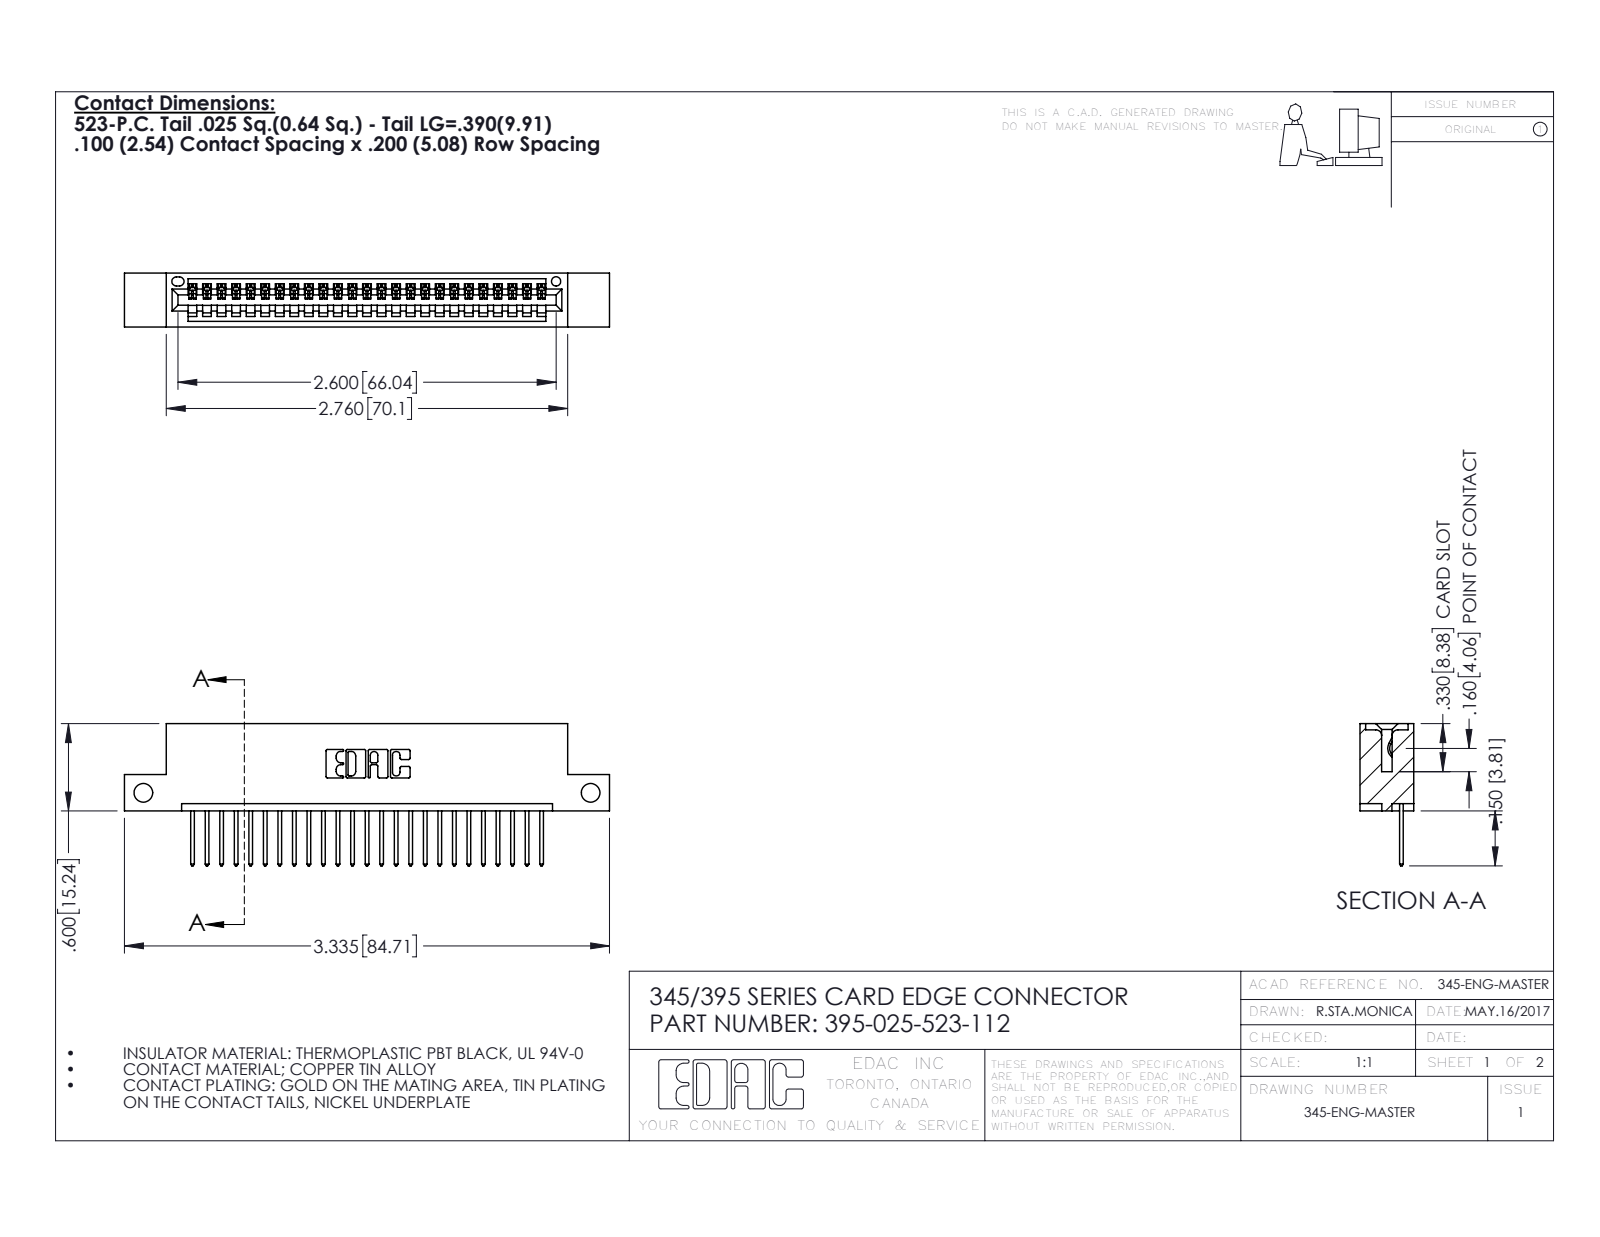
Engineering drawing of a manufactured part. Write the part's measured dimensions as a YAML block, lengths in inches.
part_name: "345-292-001_345-293-123; 395-025-523-112; 345 Part_Flush Mounting Lugs - Side Mount"
step_written_by: "SolidWorks 2016 (CONFIG_CONTROL_DESIGN)"
units: inches
bodies: {solids: 26, faces: 1576, planar: 1080, cylindrical: 496, other: 0}
overall_size: [3.335, 0.977, 0.37]
volume: 0.477
surface_area: 15.55
round_holes:
  - {diameter: 0.128, count: 2}
  - {diameter: 0.064, count: 1}
partial_cylinders:
  - {radius: 0.006, count: 50}
  - {radius: 0.01, count: 50}
  - {radius: 0.01, count: 22}
  - {radius: 0.007, count: 6}
  - {radius: 0.031, count: 6}
  - {radius: 0.026, count: 3}
  - {radius: 0.031, count: 2}
  - {radius: 0.04, count: 2}
face_to_face_distances: [0.298, 0.072, 0.2, 0.37, 0.098, 0.272, 0.025, 0.225, 0.149, 0.072]
hole_center_spacings: [3.075]
